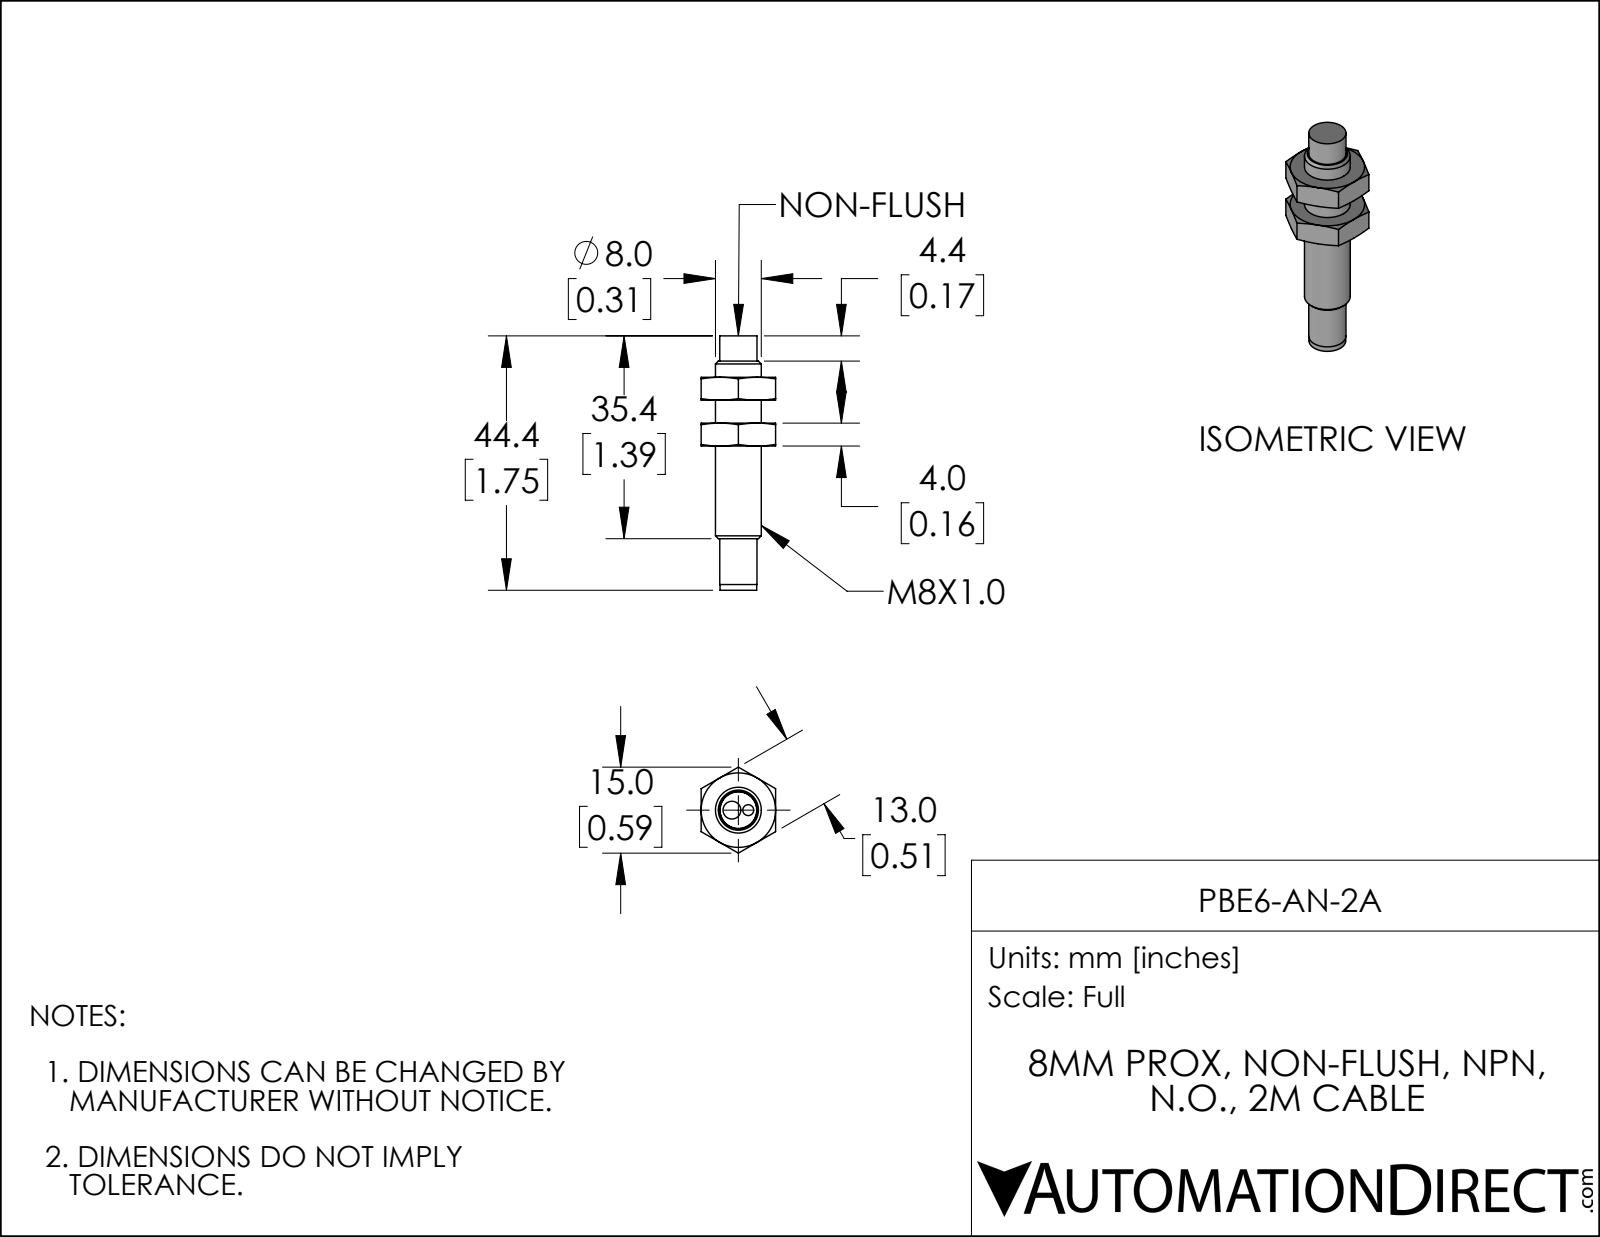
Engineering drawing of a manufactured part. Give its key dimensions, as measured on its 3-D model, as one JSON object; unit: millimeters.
{"part_name": "DSD-0262", "step_written_by": "SolidWorks 2019 (AUTOMOTIVE_DESIGN)", "units": "millimeters", "bodies": {"solids": 1, "faces": 15, "planar": 7, "cylindrical": 6, "other": 2}, "overall_size": [44.4, 8, 8], "volume_mm3": 1985, "surface_area_mm2": 1153, "round_holes": [[1.9, 1], [3.1, 1]], "round_bosses_or_shafts": [[8, 1], [6.5, 1], [6.4, 1]], "face_to_face_distances": [44.4, 43.4, 1, 35.4, 8, 9, 4.4, 31, 39, 40], "hole_center_spacings": [2.85]}
